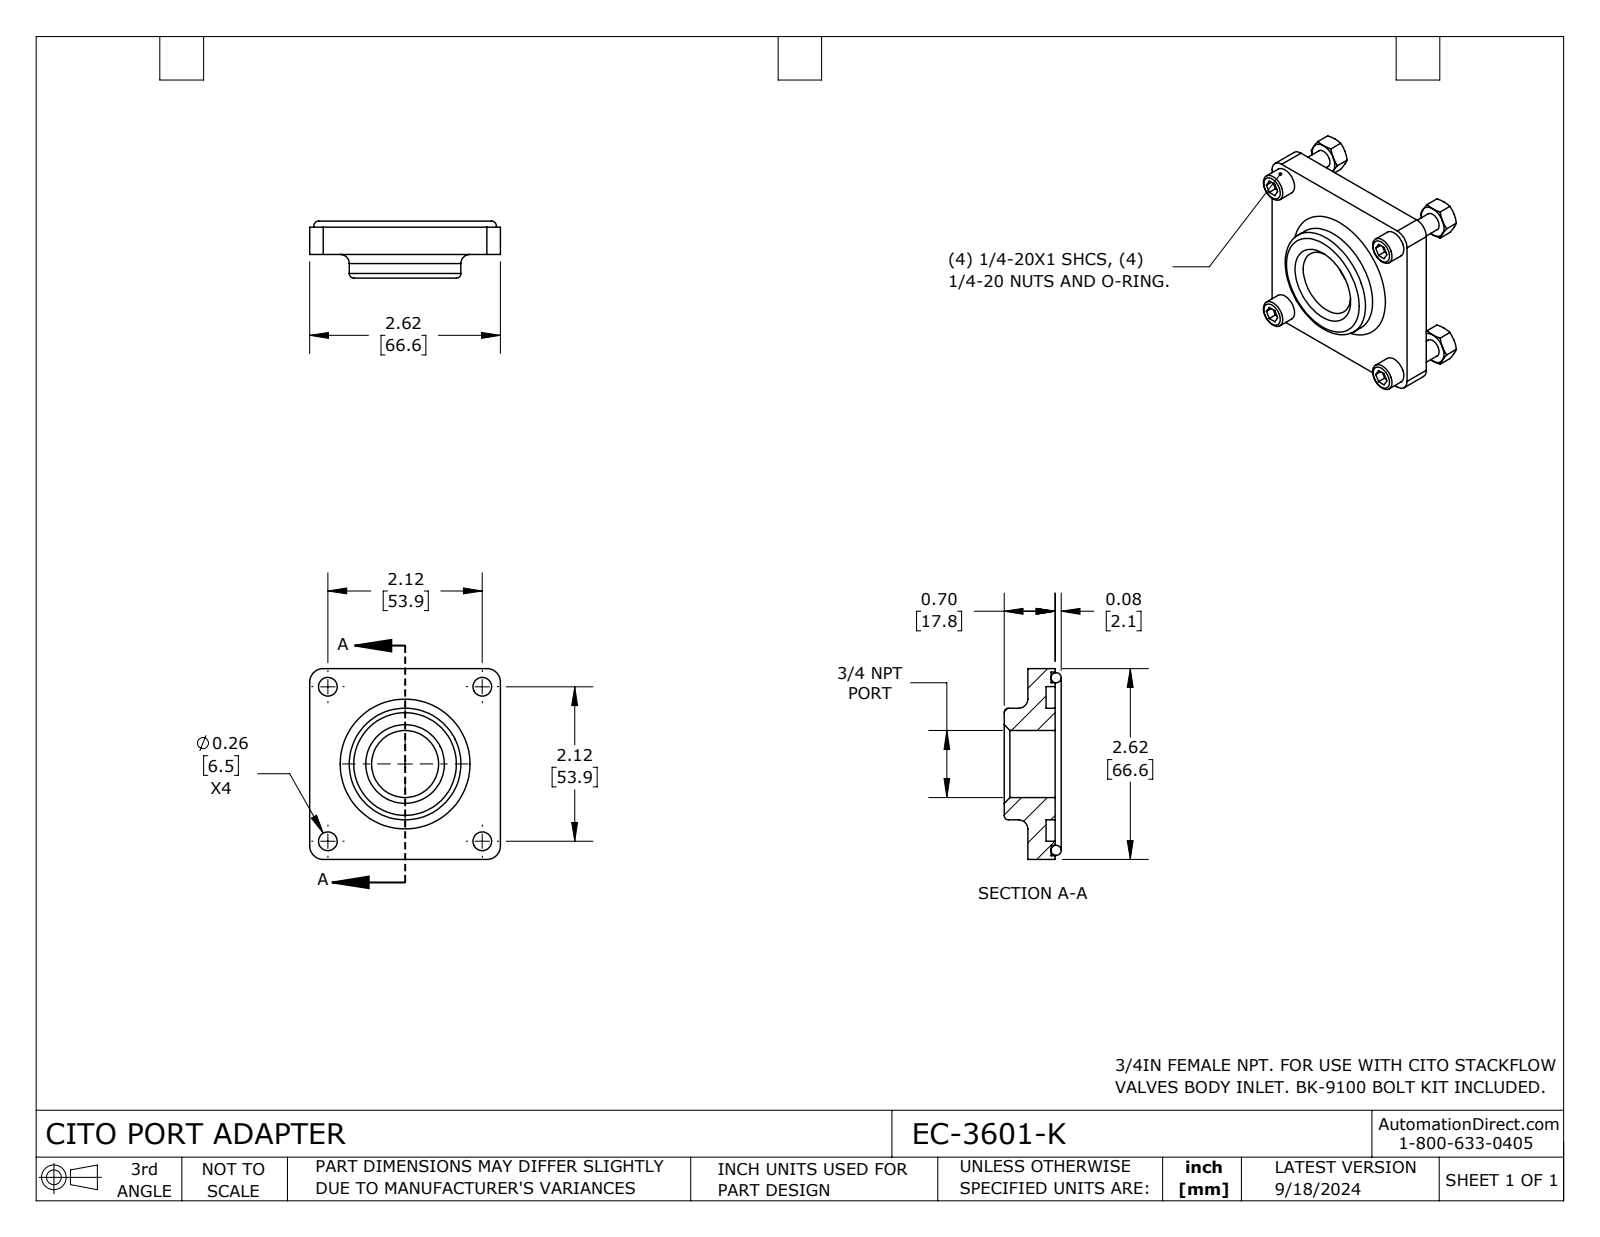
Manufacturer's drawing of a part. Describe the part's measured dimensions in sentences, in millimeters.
The part is named "EC-3601-K". Its 3-D file was written by "SolidWorks 2023 (CONFIG_CONTROL_DESIGN)". It is 2 solids with 46 faces: 11 planar, 25 cylindrical and 10 other. Overall it measures 66.6 by 66.6 by 19.9 millimeters. Its volume is 40 510 cubic millimeters and its surface area 16 510 square millimeters. Round holes: 4 of diameter 6.5, 1 of diameter 23.4, 1 of diameter 54, 1 of diameter 64.1. Round bosses or shafts: 1 of diameter 56.7, 1 of diameter 39. Partial cylindrical surfaces (rounded edges, fillets, slot ends): 3 of radius 4.8, 1 of radius 4.7. The main face-to-face distances are 9.5, 6.4, 3.2, 66.6, 8.1, 1.8, 1.4, 8.3, 14.6, 16.4. The hole center spacings are 38.2, 53.9, 76.3.
